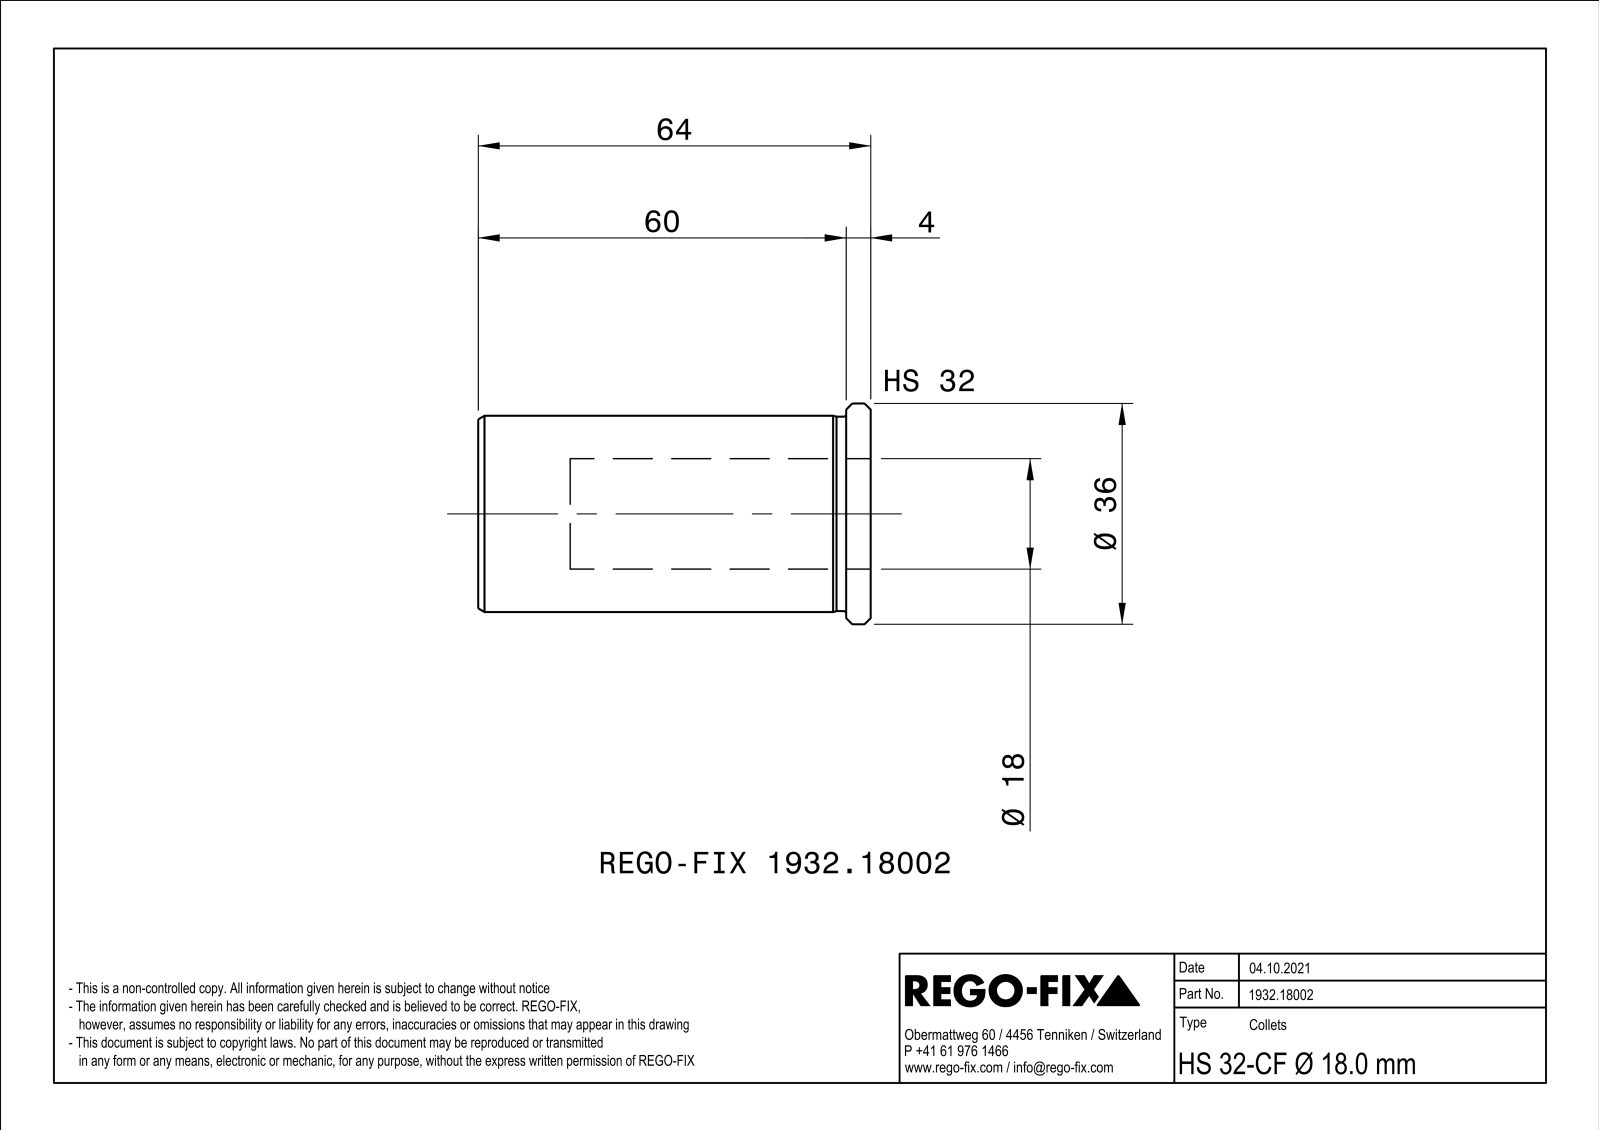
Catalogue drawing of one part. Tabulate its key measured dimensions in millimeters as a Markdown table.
| quantity | value |
| --- | --- |
| part name | NOCUT |
| STEP written by | SIEMENS PLM Software Solid Edge ST10 (AUTOMOTIVE_DESIGN) |
| units | millimeters |
| bodies | 1 solid, 80 faces (14 planar, 26 cylindrical, 40 other) |
| overall size | 64 × 35.99 × 35.99 |
| volume | 30 414 mm³ |
| surface area | 14 214 mm² |
| round holes (diameter × count) | 18 × 1, 26.5 × 1 |
| round bosses / shafts (diameter × count) | 36 × 1, 32 × 1, 31.7 × 1 |
| partial cylindrical surfaces (radius × count) | 0.5 × 6, 0.75 × 4 |
| main face-to-face distances | 1, 64, 4, 60 |
